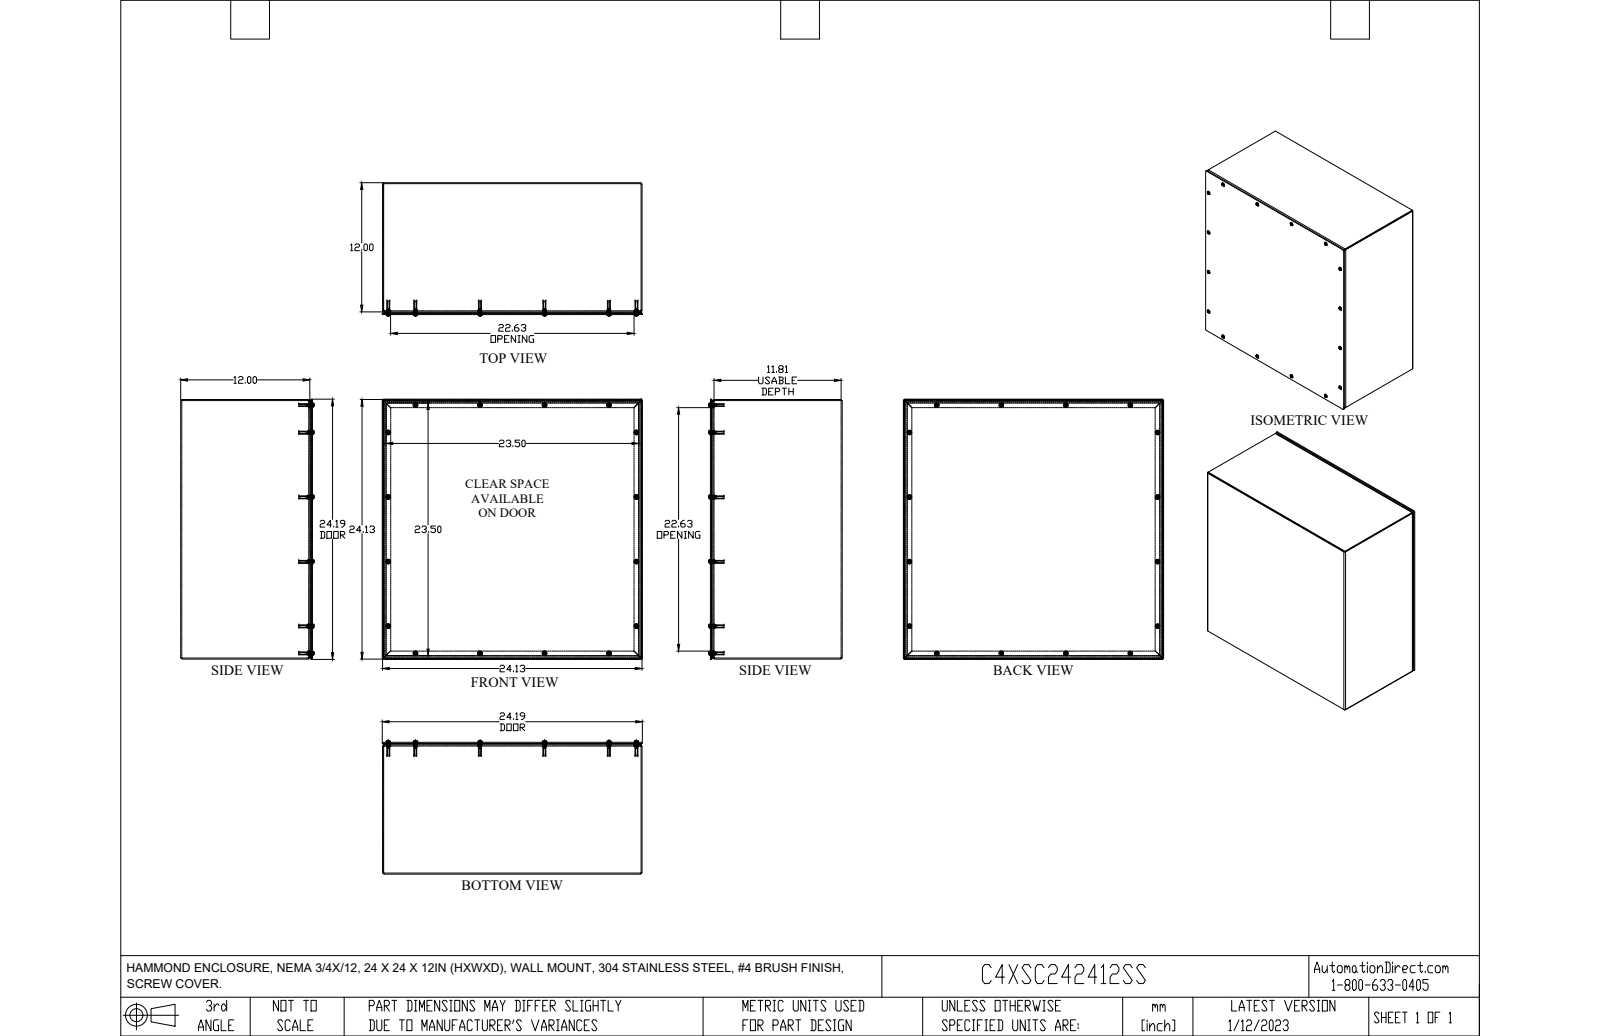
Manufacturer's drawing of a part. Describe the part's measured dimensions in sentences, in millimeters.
The part is named "C3SC242412GY". Its 3-D file was written by "SolidWorks 2021 (AUTOMOTIVE_DESIGN)". It is 51 solids with 1476 faces: 920 planar, 272 cylindrical and 284 other. Overall it measures 614.4 by 614.4 by 315 millimeters. Its volume is 3 300 000 cubic millimeters and its surface area 3 172 000 square millimeters. Round holes: 16 of diameter 4, 16 of diameter 4.1, 16 of diameter 6.4. Round bosses or shafts: 16 of diameter 11.2, 16 of diameter 9.9, 16 of diameter 6.1, 16 of diameter 4.8, 16 of diameter 3.8, 12 of diameter 7, 4 of diameter 7. Partial cylindrical surfaces (rounded edges, fillets, slot ends): 16 of radius 4.1, 8 of radius 1, 8 of radius 2.8, 8 of radius 3.2, 4 of radius 3.2, 4 of radius 9.5. The main face-to-face distances are 1.8, 3.2, 311.2, 308, 309.4, 306.2, 612.9, 611.1, 609.3, 611.1. The hole center spacings are 152.4, 605.6, 226.2, 304.8, 374.8, 428.2, 525.6, 564.9.
